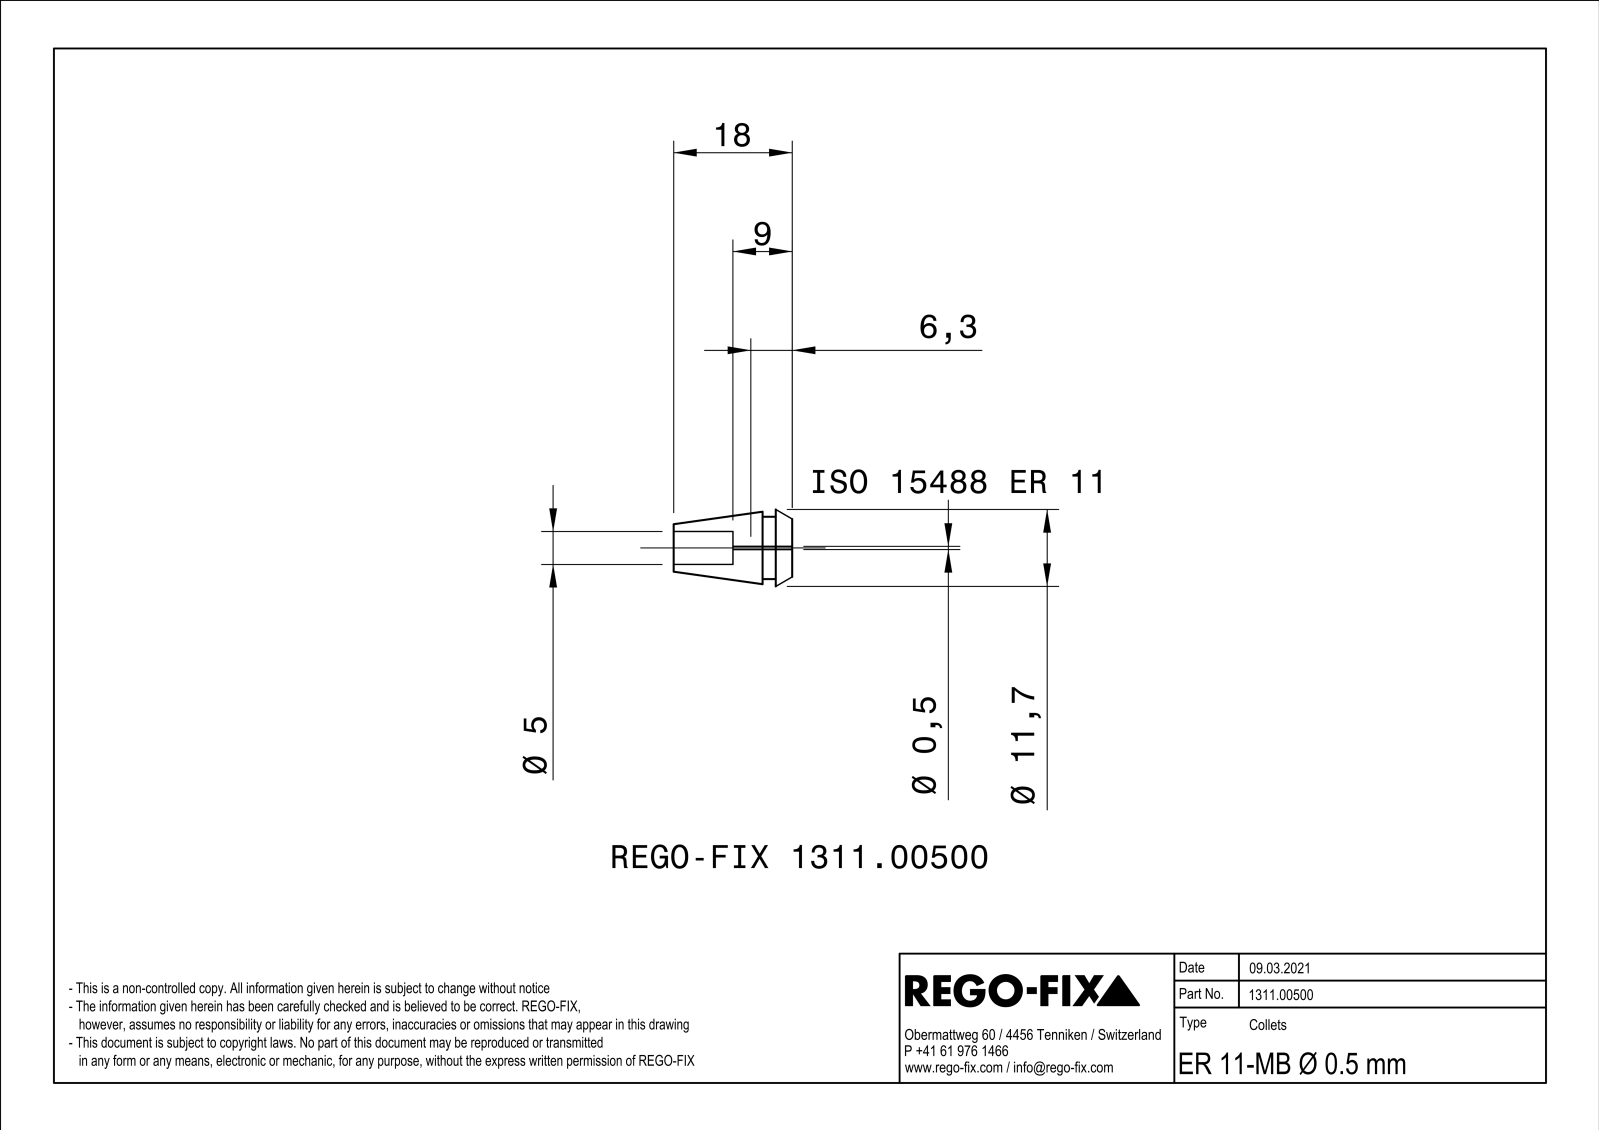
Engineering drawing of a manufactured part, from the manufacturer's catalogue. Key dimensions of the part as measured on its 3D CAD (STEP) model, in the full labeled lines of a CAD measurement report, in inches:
Part name (STEP PRODUCT): NOCUT
STEP written by: SIEMENS PLM Software Solid Edge ST10 (AUTOMOTIVE_DESIGN)
Units: inches
Bodies: 1 solid, 91 faces (26 planar, 19 cylindrical, 46 other)
Overall size (bounding box): 0.709 × 0.439 × 0.438
Volume: 0.055 in³ · Surface area: 1.869 in²
Round holes (diameter × count): ⌀0.059 ×3, ⌀0.197 ×1
Round bosses / shafts (diameter × count): ⌀0.374 ×1
Partial cylindrical surfaces — rounded edges, fillets, slot ends (radius × count): R0.984 ×3, R0.01 ×1
Main face-to-face distances: 0.031, 0.02, 0.177, 0.354, 0.098, 0.709, 0.61, 0.079, 0.531, 0.256
Hole centre spacings: 0.067, 0.116
